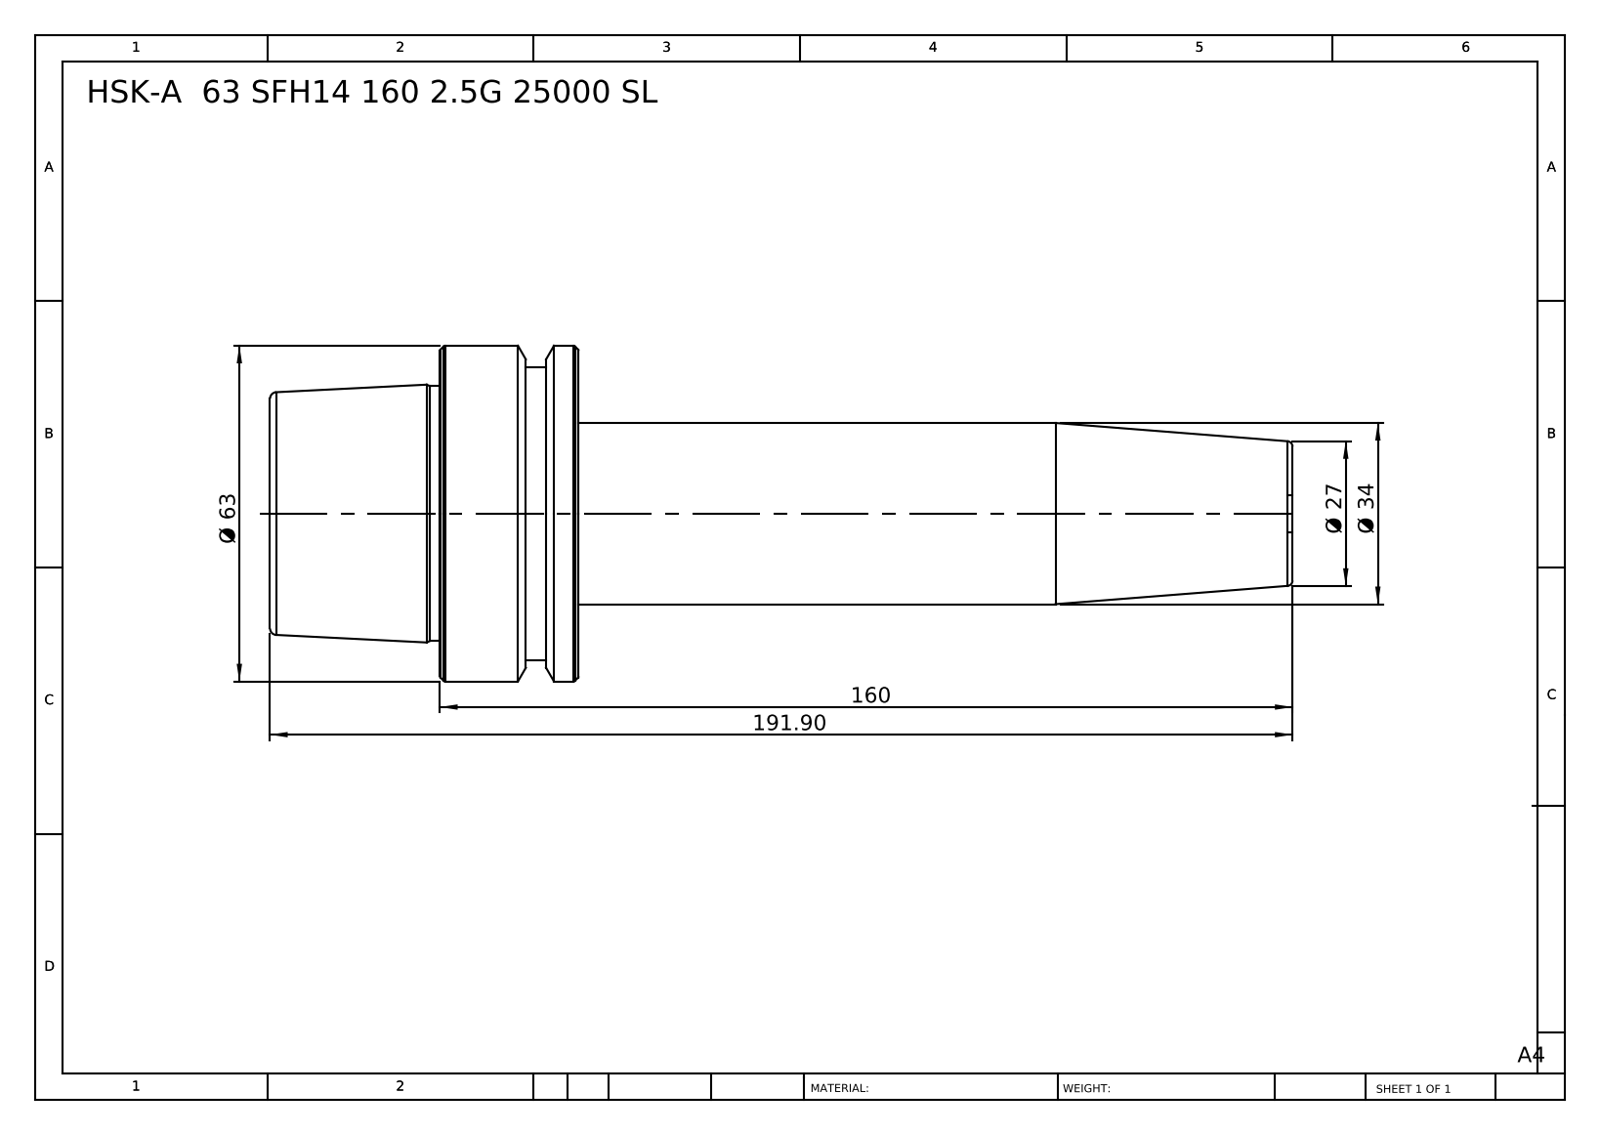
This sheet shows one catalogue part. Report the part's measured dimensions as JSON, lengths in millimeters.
{"part_name": "HSK-A 63 SFH14 160 2.5G 25000 SL", "step_written_by": "SolidWorks 2014 (CONFIG_CONTROL_DESIGN)", "units": "millimeters", "bodies": {"solids": 1, "faces": 46, "planar": 6, "cylindrical": 10, "other": 30}, "overall_size": [191.9, 63, 63], "volume_mm3": 246500, "surface_area_mm2": 30120, "round_bosses_or_shafts": [[63, 1], [55, 1], [47.78, 1], [34, 1]], "face_to_face_distances": [57.9, 26, 31.9, 134, 160, 191.9, 140.1, 6.1, 19.9, 51.8]}
